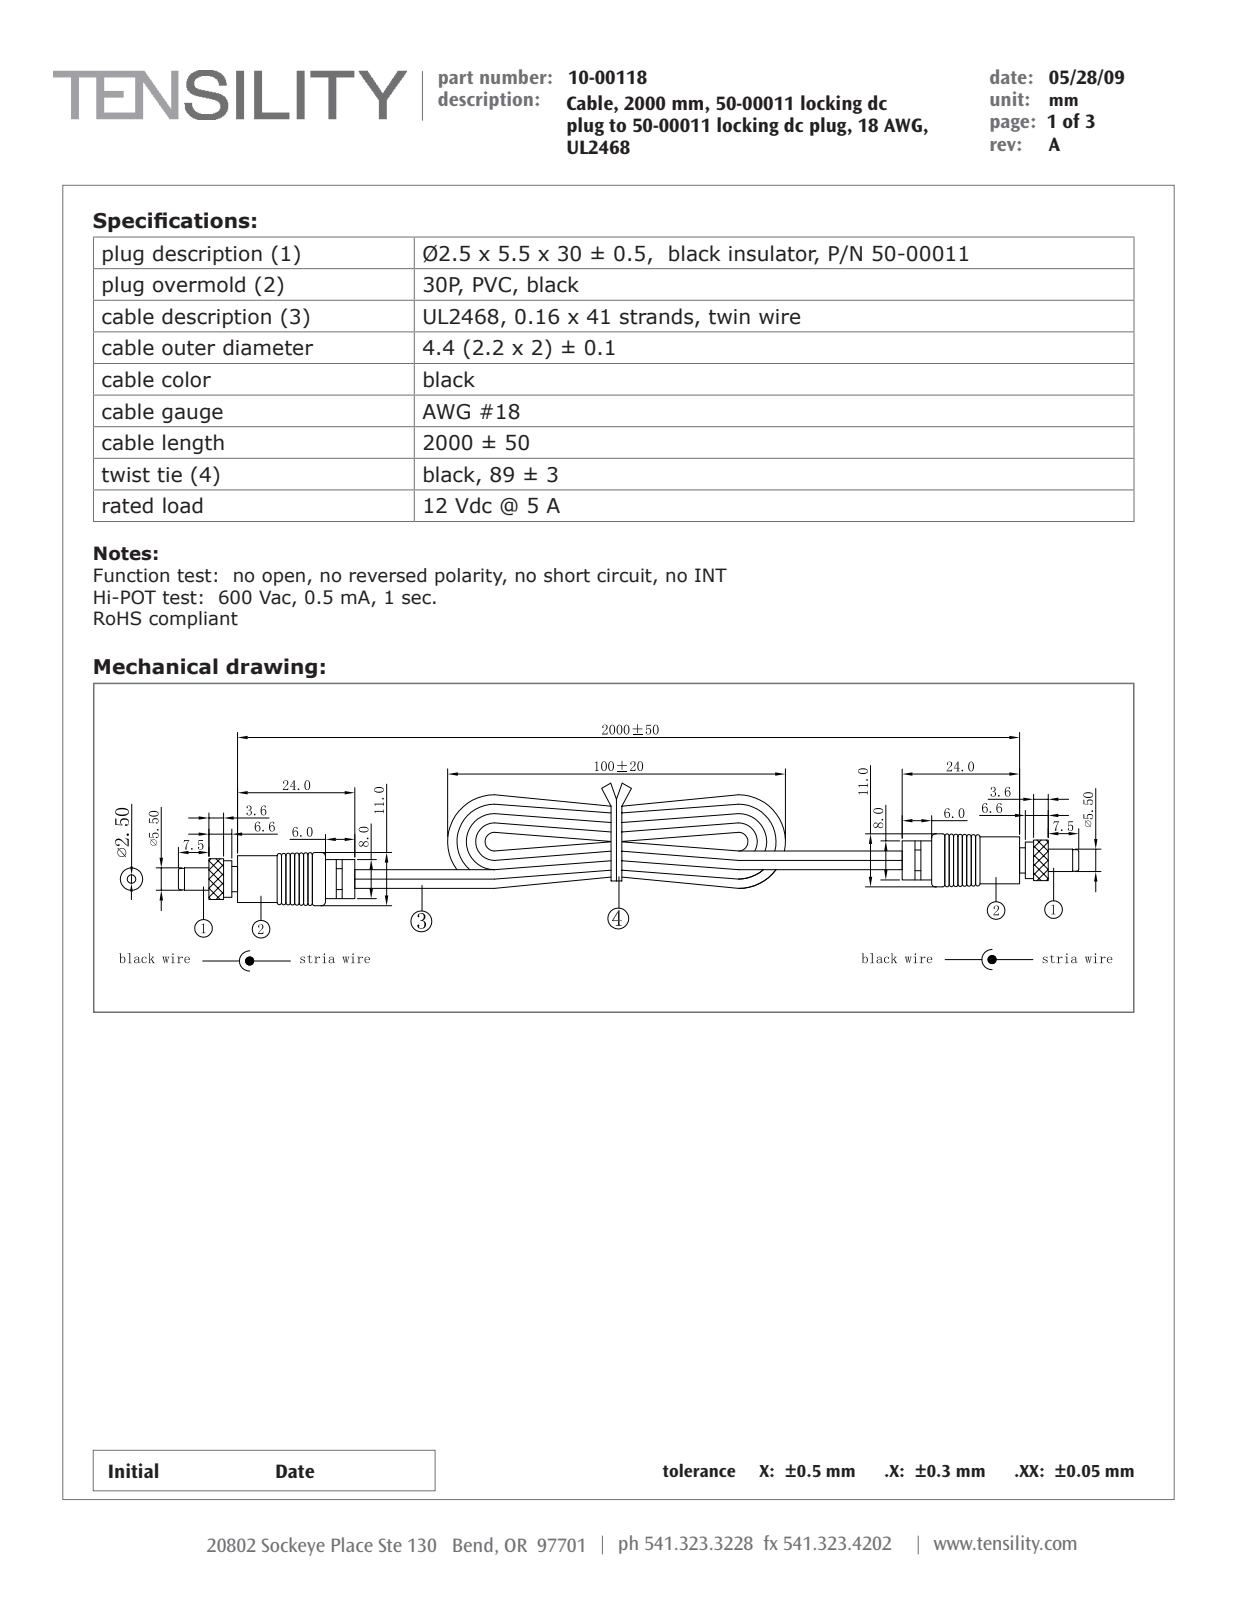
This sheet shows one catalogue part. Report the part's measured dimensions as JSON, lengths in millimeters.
{"part_name": "50-00011 pin; 50-00011 locking ring; 50-00011 interior shell; 10-00118 (+6 more)", "step_written_by": "SolidWorks 2015 (CONFIG_CONTROL_DESIGN)", "units": "millimeters", "bodies": {"solids": 22, "faces": 2678, "planar": 757, "cylindrical": 481, "other": 1440}, "overall_size": [221.6, 11, 11], "volume_mm3": 6093, "surface_area_mm2": 10658, "round_holes": [[1.6, 1], [2.16, 1], [2.5, 1], [3, 1], [3.25, 1], [4.25, 1], [5.04, 1], [5.44, 1], [5.5, 1], [5.65, 1], [6.4, 1], [7.25, 1]], "round_bosses_or_shafts": [[11, 2], [10, 2], [2.2, 2], [8, 1], [7, 1], [6.2, 1], [6, 1], [5.48, 1]], "partial_cylinders_radius": [[0.2, 12], [0.55, 4], [3.92, 1]], "face_to_face_distances": [24, 165.8, 19.9, 169.9, 4.1, 145.9, 21.4, 168.4, 1.5, 148.5]}
